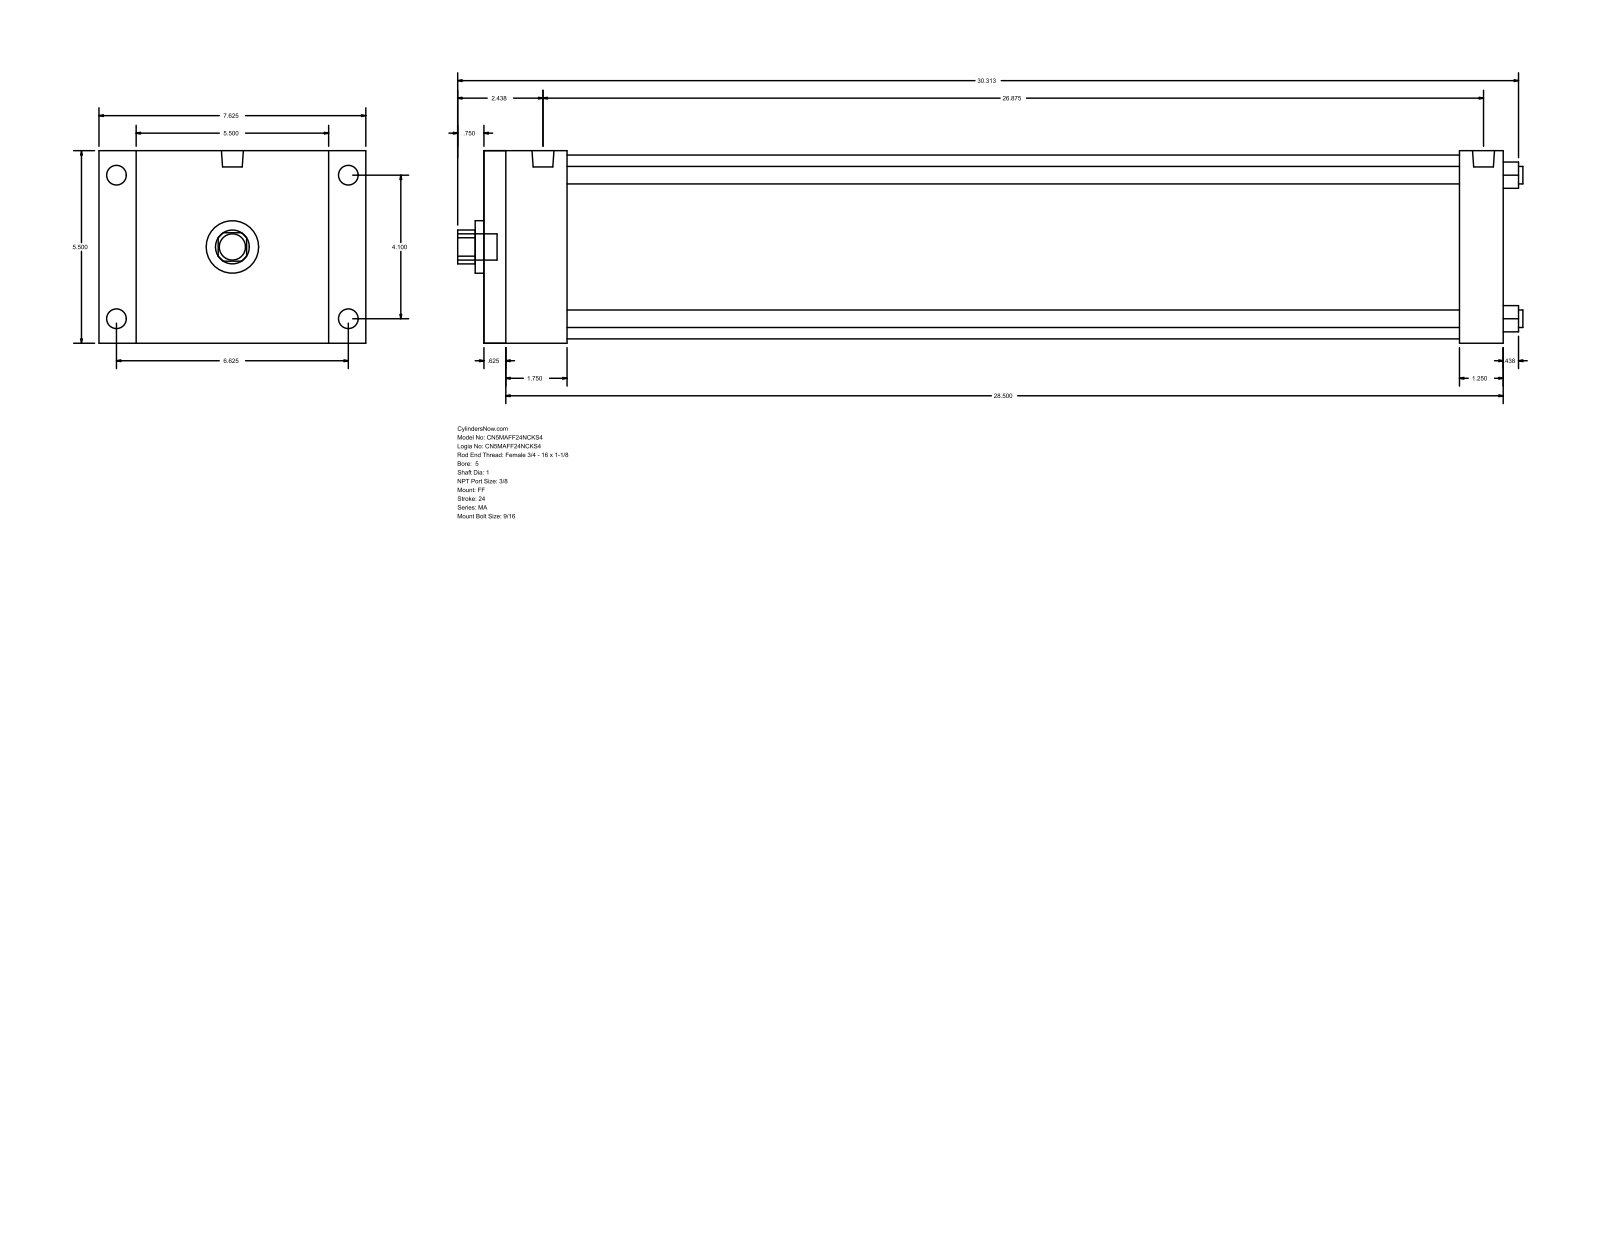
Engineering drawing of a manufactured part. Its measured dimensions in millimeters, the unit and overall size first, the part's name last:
Units: millimetres
Overall size (bounding box): 773.11 × 193.68 × 139.7
Round holes (diameter × count): ⌀12.7 ×4, ⌀25.4 ×1, ⌀38.1 ×1, ⌀133.35 ×1
Round bosses / shafts (diameter × count): ⌀14.29 ×4, ⌀11.11 ×4, ⌀15.93 ×2, ⌀19.05 ×1
Partial cylindrical surfaces — rounded edges, fillets, slot ends (radius × count): R12.29 ×1
Main face-to-face distances: 139.7, 739.78, 15.87, 723.91, 708.03, 692.16, 31.75, 60.33, 44.46, 647.7
Hole centre spacings: 73.64, 104.14, 147.28
Bodies: 0 solids, 92 faces (64 planar, 28 cylindrical, 0 other)
Part name (STEP PRODUCT): MA_FF__0500_1
STEP written by: GSSL Pune (CONFIG_CONTROL_DESIGN)
